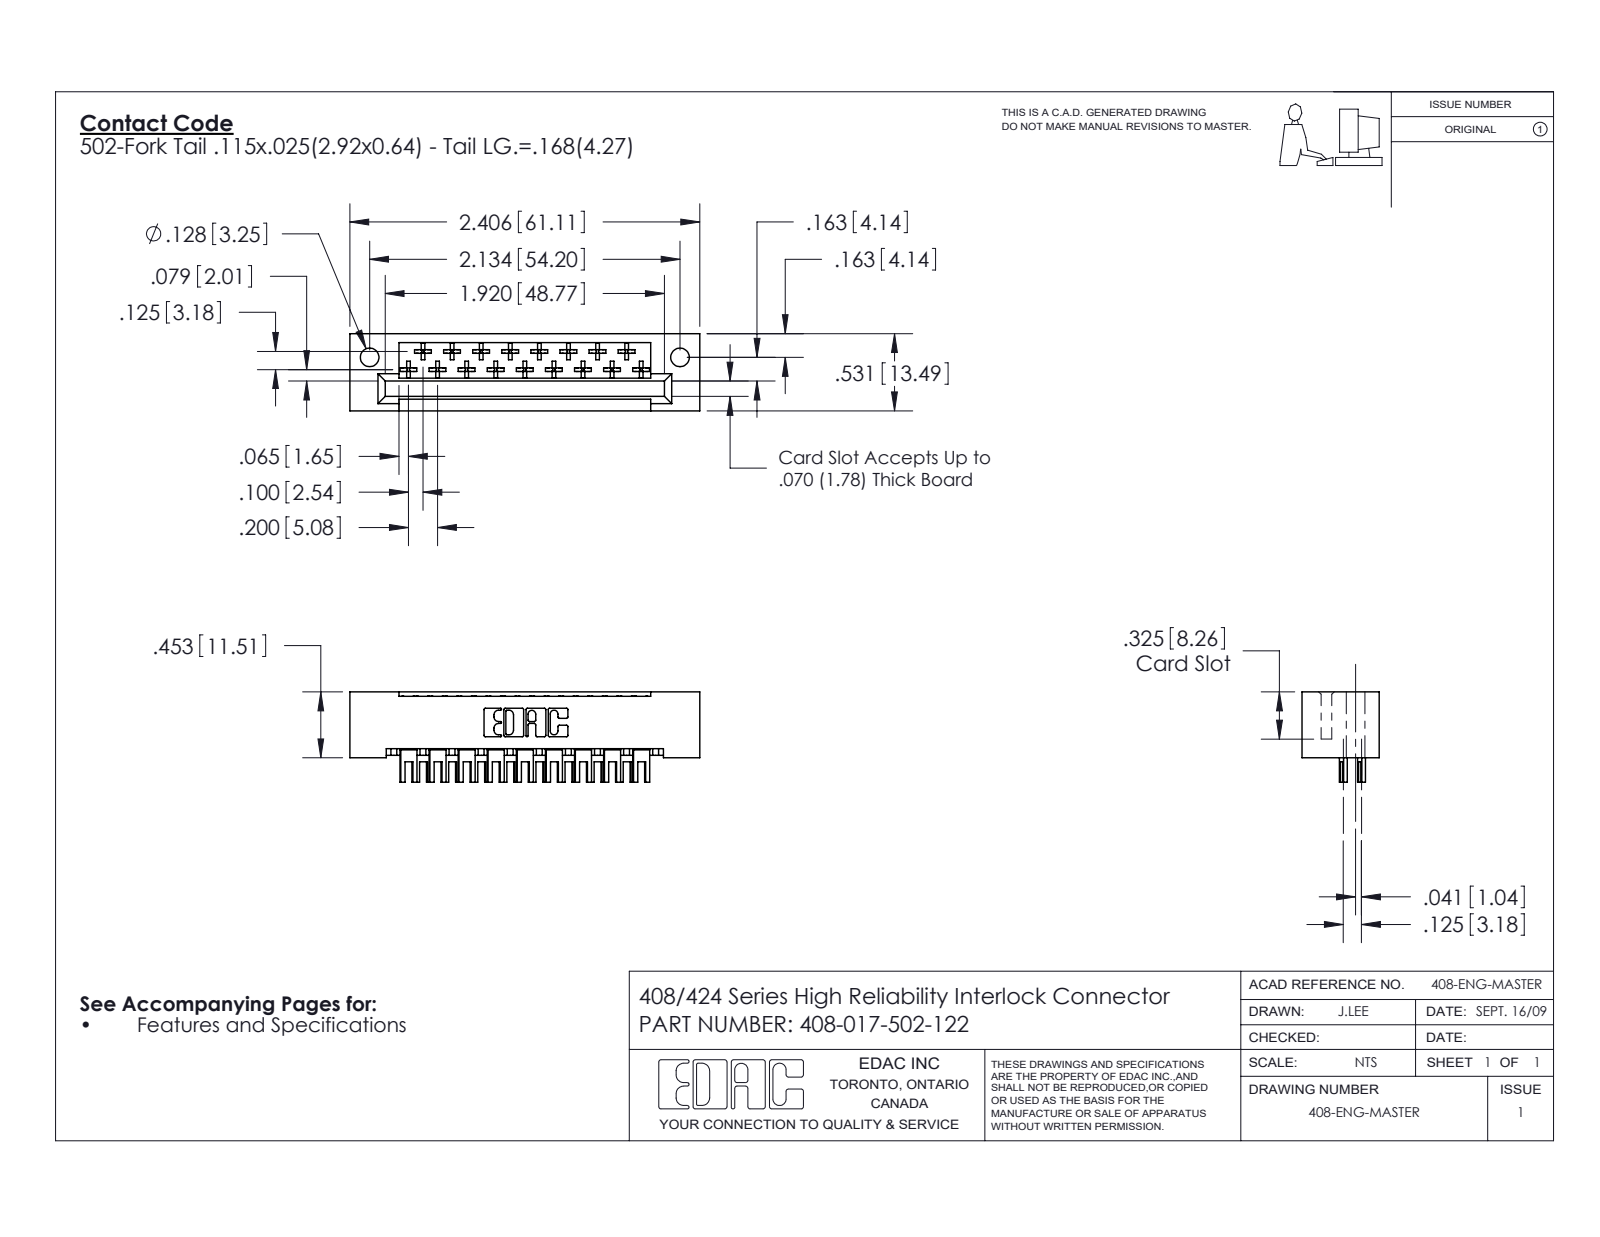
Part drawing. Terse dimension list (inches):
name: 408-017-502-122; 408 Part_017 - 1; 408-290-001_408-290-102
written by: SolidWorks 2016 (CONFIG_CONTROL_DESIGN)
unit: in
bodies: 18 solids, 1028 faces (776 planar, 184 cylindrical, 68 other)
size: 2.406 × 0.621 × 0.531
volume: 0.422 in³; area: 12.51 in²
holes: 2× ⌀0.128
rounds: 102× R0.01, 22× R0.01, 19× R0.02, 6× R0.007, 6× R0.031, 3× R0.026
face distances: 0.1, 0.296, 0.025, 0.531, 0.025, 0.125, 0.272, 0.235, 0.259, 0.217
hole spacings: 2.134
